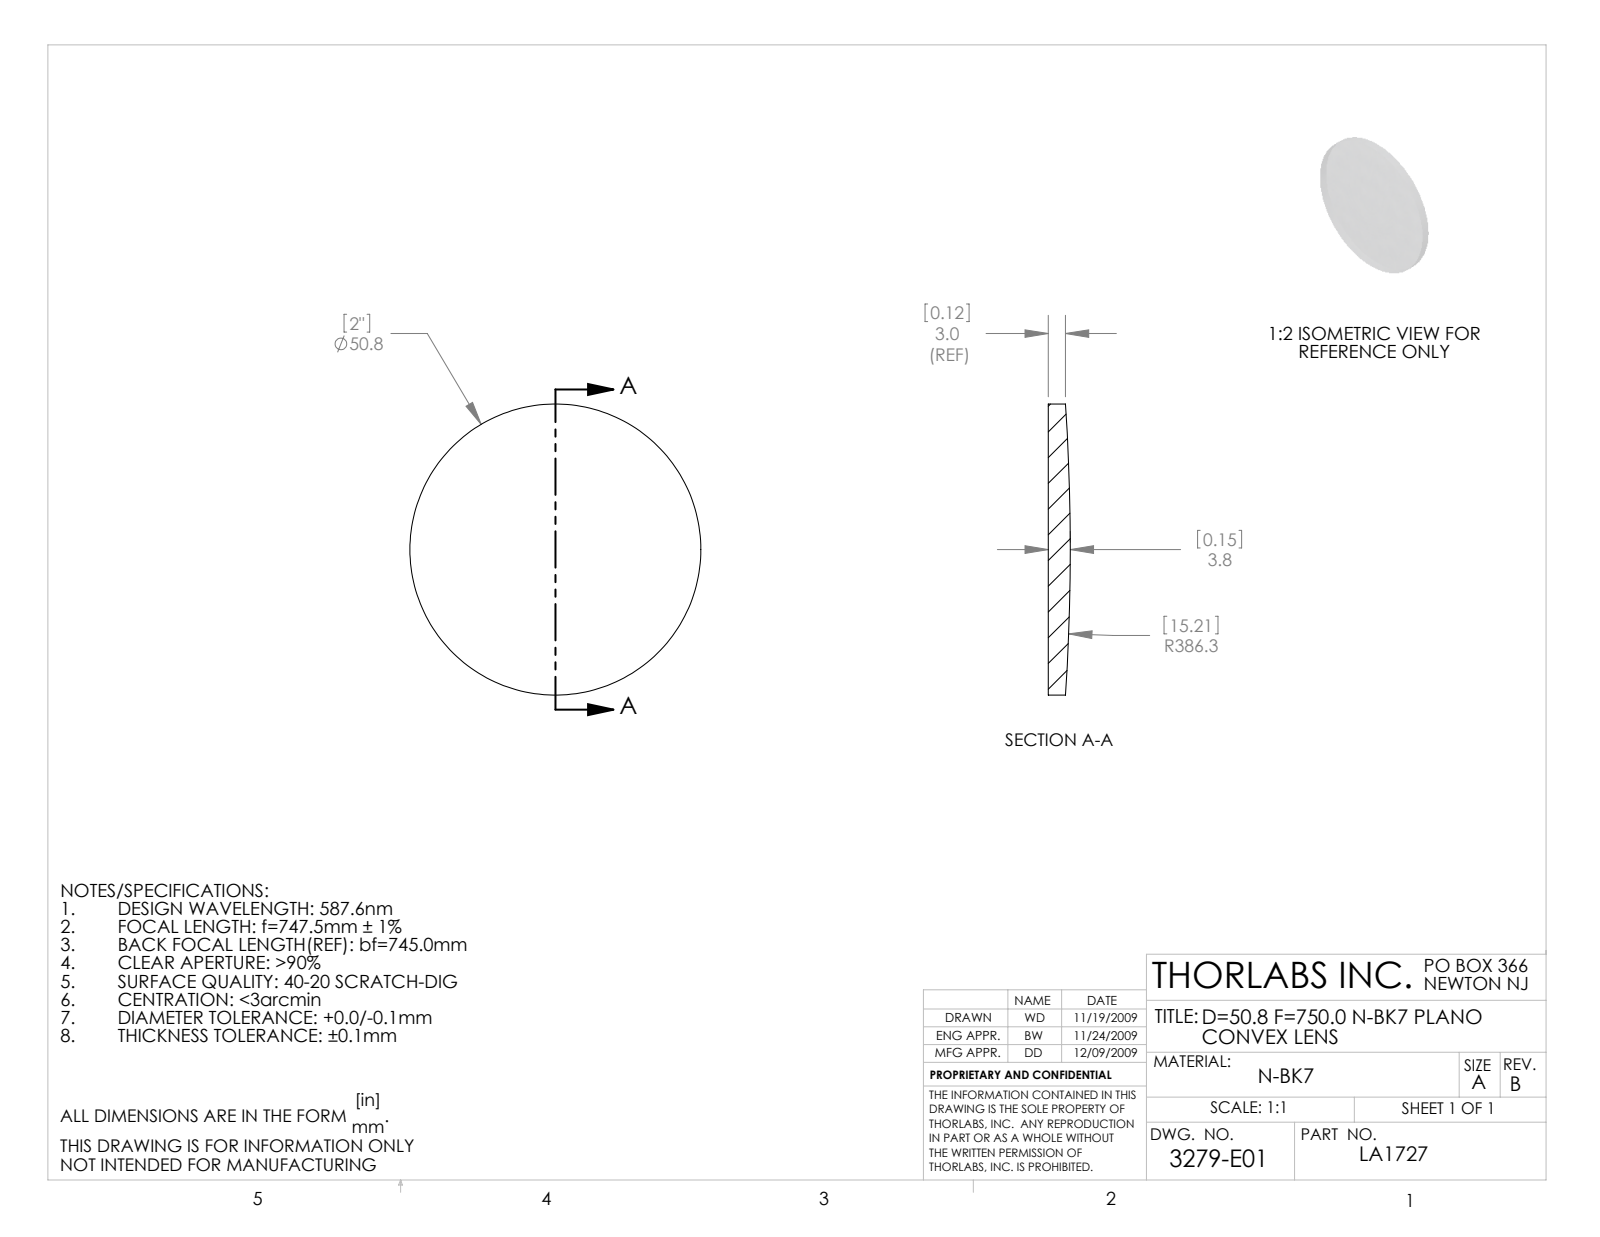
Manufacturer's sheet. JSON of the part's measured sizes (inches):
{"part_name": "3279-E0W", "step_written_by": "SolidWorks 2009 (AUTOMOTIVE_DESIGN)", "units": "inches", "bodies": {"solids": 1, "faces": 5, "planar": 1, "cylindrical": 2, "other": 2}, "overall_size": [2, 2, 0.151], "volume_in3": 0.422, "surface_area_in2": 7.028, "round_bosses_or_shafts": [[2, 1]]}
